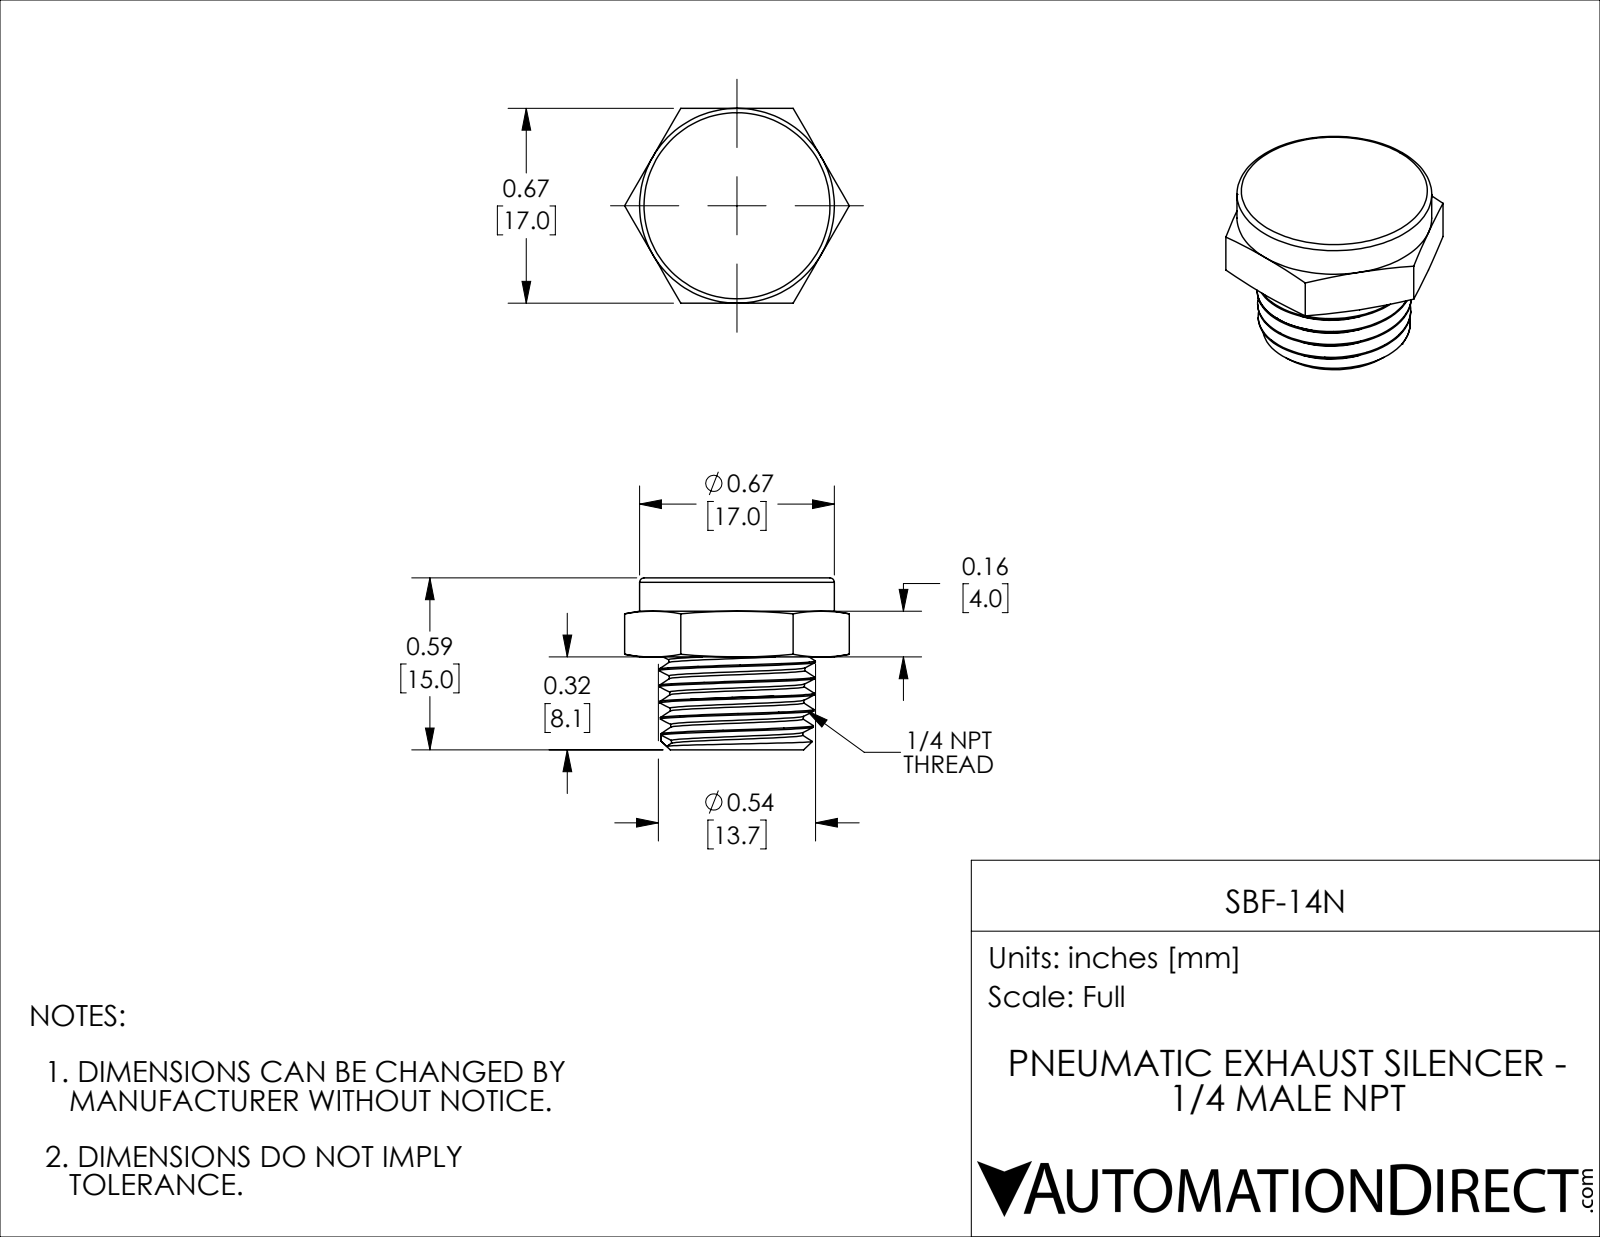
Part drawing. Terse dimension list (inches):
name: SBF-14N
written by: SolidWorks 2021 (CONFIG_CONTROL_DESIGN)
unit: in
bodies: 1 solid, 49 faces (11 planar, 4 cylindrical, 34 other)
size: 0.773 × 0.669 × 0.591
volume: 0.133 in³; area: 2.53 in²
holes: 1× ⌀0.314
bosses: 1× ⌀0.669
face distances: 0.669, 0.272, 0.319, 0.591, 0.375, 0.056, 0.216
